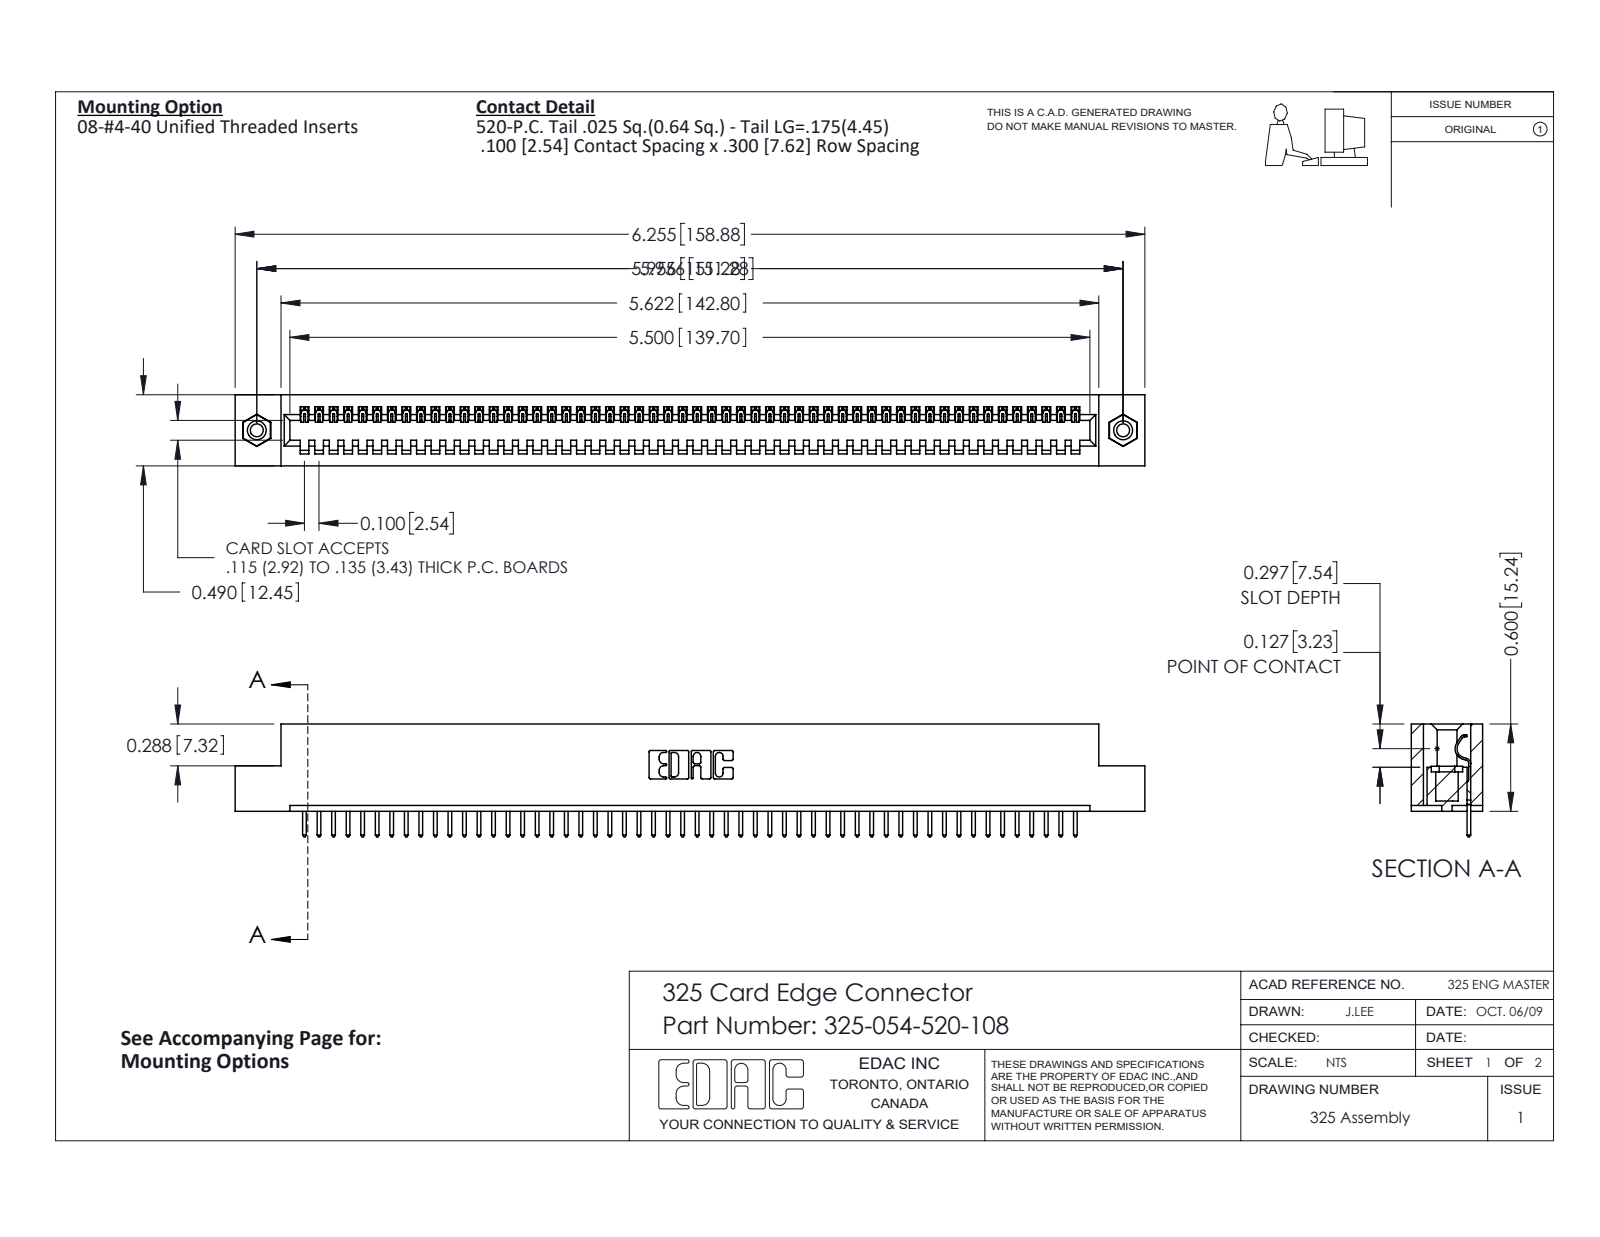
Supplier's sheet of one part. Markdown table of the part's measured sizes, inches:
| quantity | value |
| --- | --- |
| part name | 325 Part_TI; 325-054-520-108; 325-292-001_325-293-120; 345-250-001_345-250-003-102 |
| STEP written by | SolidWorks 2016 (CONFIG_CONTROL_DESIGN) |
| units | inches |
| bodies | 57 solids, 3306 faces (2370 planar, 920 cylindrical, 16 other) |
| overall size | 6.255 × 0.775 × 0.49 |
| volume | 1.228 in³ |
| surface area | 33.53 in² |
| round holes (diameter × count) | 0.089 × 2, 0.125 × 2, 0.16 × 2 |
| round bosses / shafts (diameter × count) | 0.155 × 2 |
| partial cylindrical surfaces (radius × count) | 0.006 × 108, 0.01 × 108, 0.01 × 22, 0.007 × 6, 0.031 × 6, 0.026 × 3, 0.014 × 1, 0.022 × 1 |
| main face-to-face distances | 0.083, 0.407, 0.49, 0.3, 0.107, 0.383, 0.025, 0.325, 0.56, 0.263 |
| hole center spacings | 5.956 |
